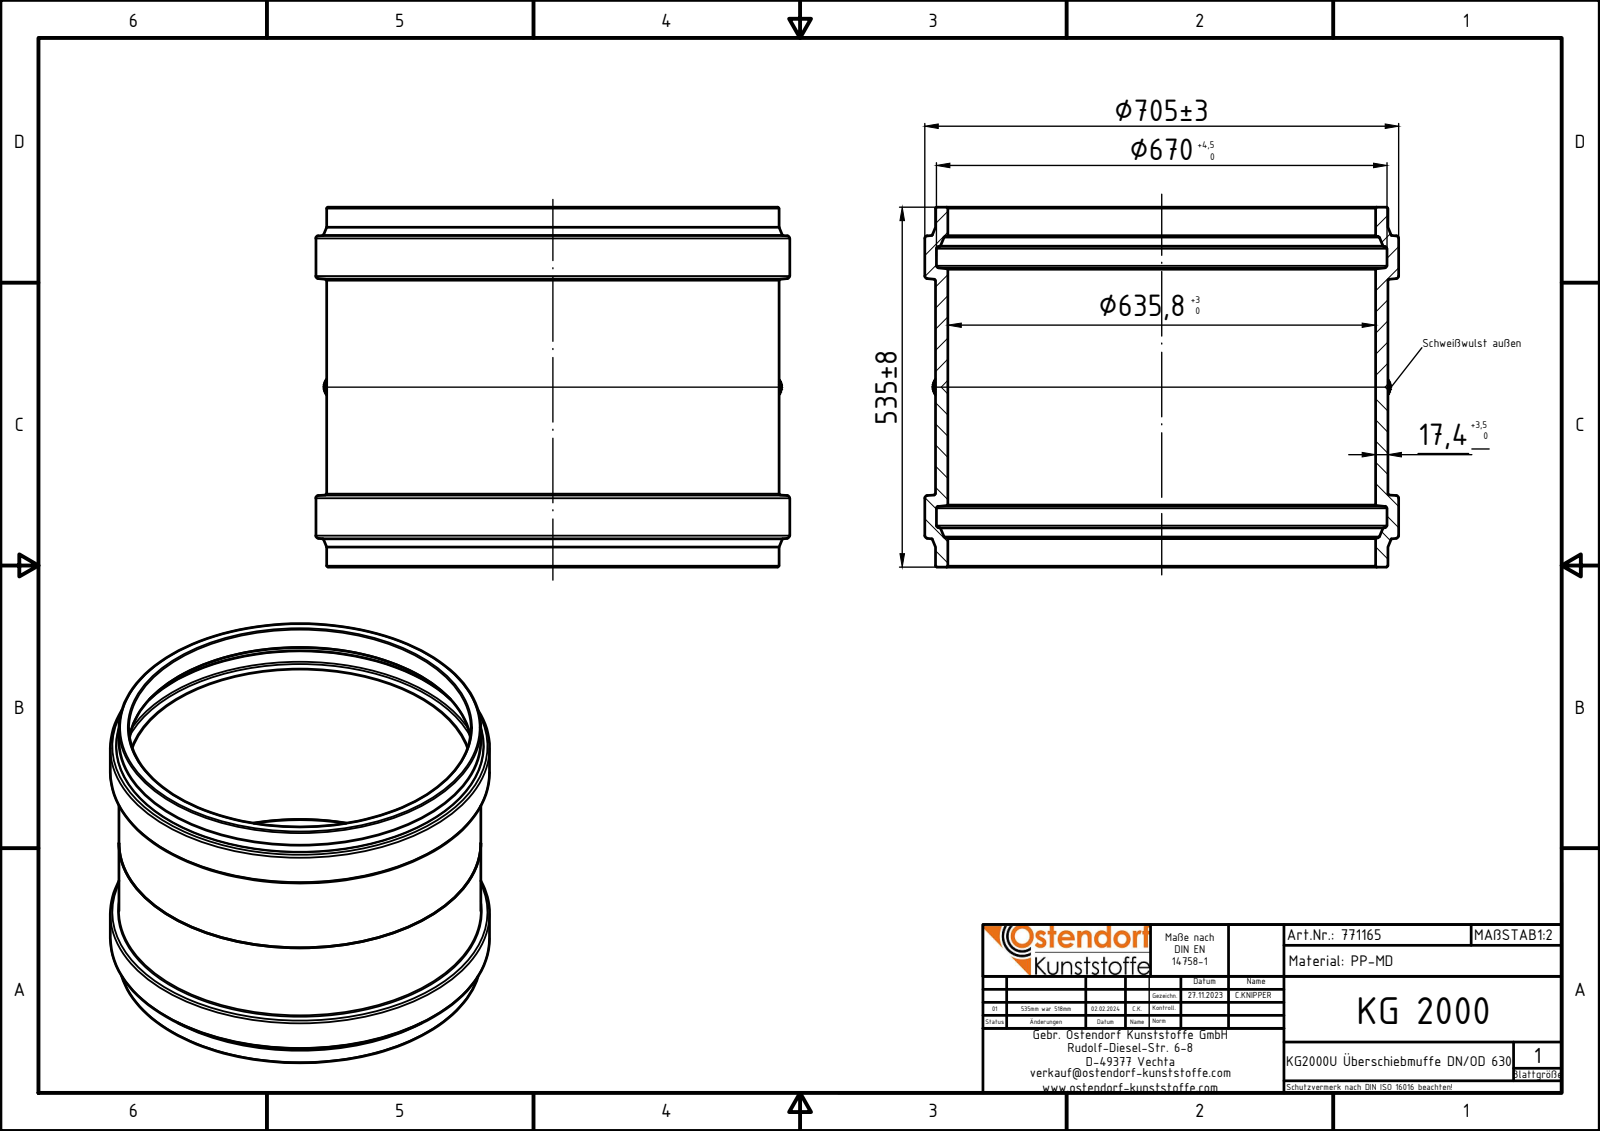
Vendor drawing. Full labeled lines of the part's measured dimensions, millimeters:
Part name (STEP PRODUCT): 771165z
STEP written by: Autodesk Inventor 2024 (AUTOMOTIVE_DESIGN)
Units: millimetres
Bodies: 2 solids, 54 faces (4 planar, 12 cylindrical, 38 other)
Overall size (bounding box): 704.8 × 704.8 × 535
Volume: 22 060 000 mm³ · Surface area: 2 557 000 mm²
Round holes (diameter × count): ⌀635.8 ×1, ⌀670 ×1
Round bosses / shafts (diameter × count): ⌀704.8 ×1, ⌀672.6 ×1
Main face-to-face distances: 267.5, 535
